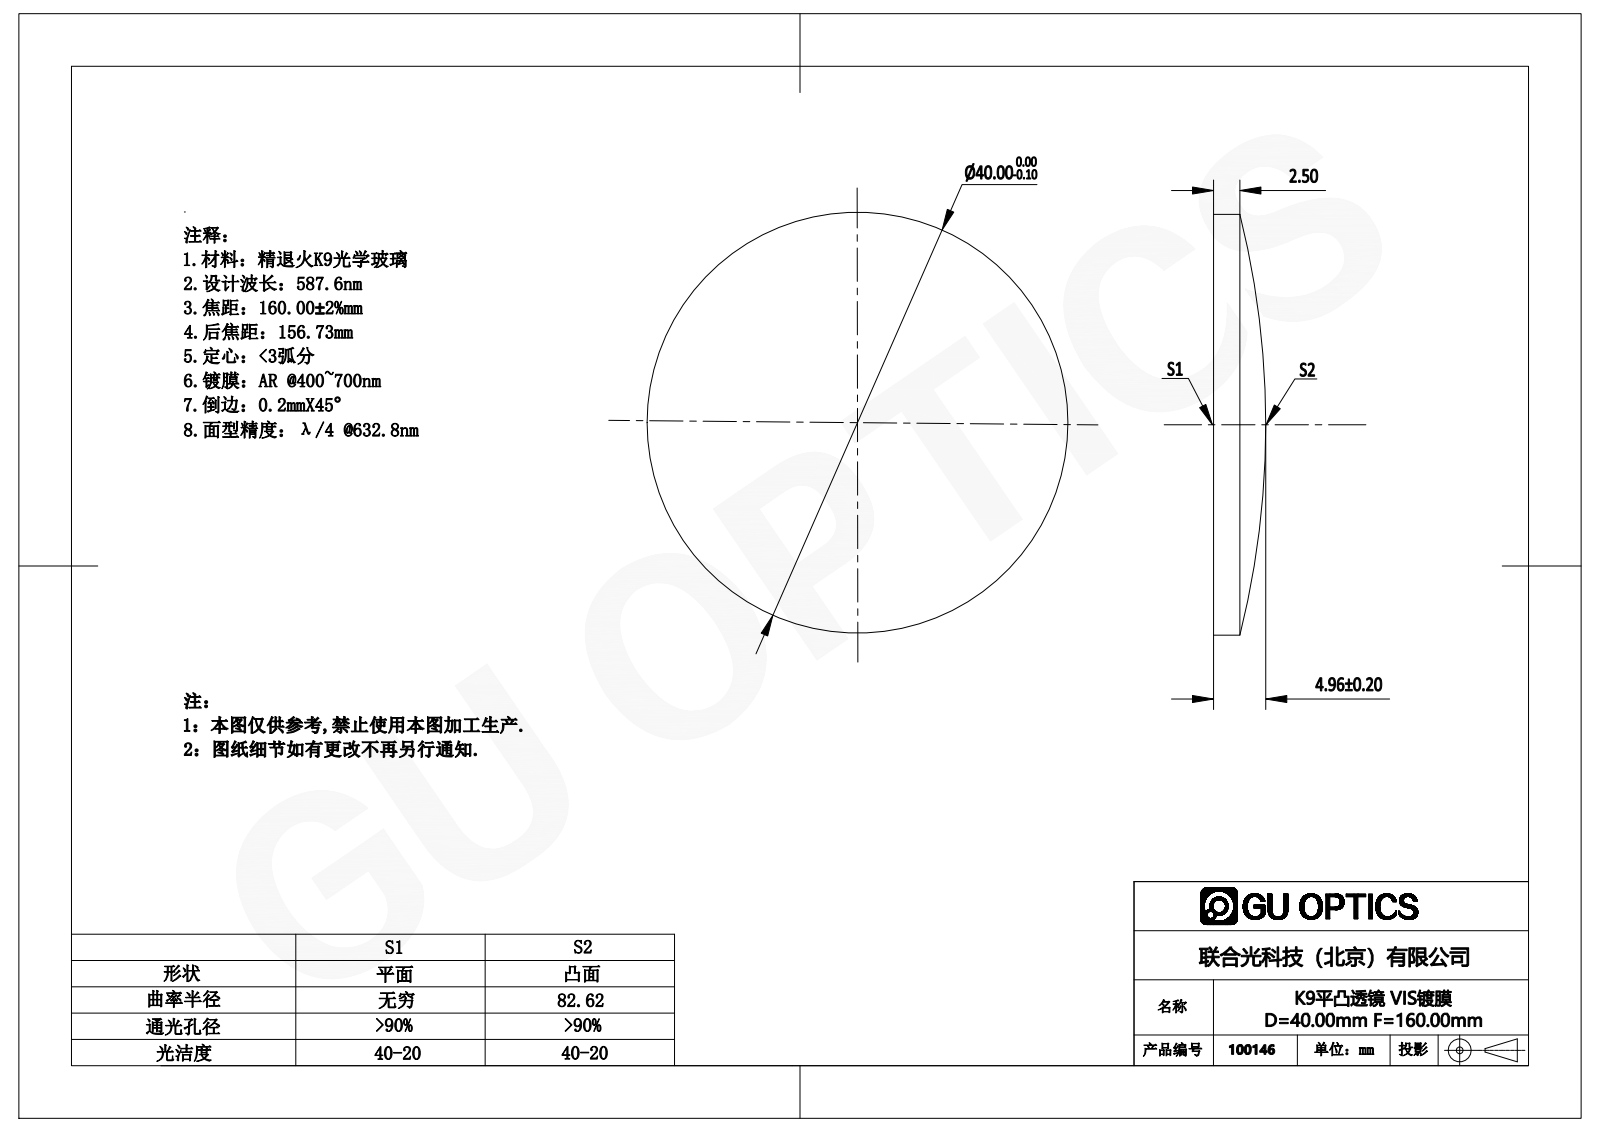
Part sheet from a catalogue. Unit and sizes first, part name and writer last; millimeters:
Units: millimetres
Overall size (bounding box): 40 × 40 × 4.96
Round bosses / shafts (diameter × count): ⌀40 ×1
Volume: 4 695 mm³ · Surface area: 2 846 mm²
Bodies: 1 solid, 5 faces (1 planar, 2 cylindrical, 2 other)
Part name (STEP PRODUCT): 100146
STEP written by: SolidWorks 2016 (AUTOMOTIVE_DESIGN)
